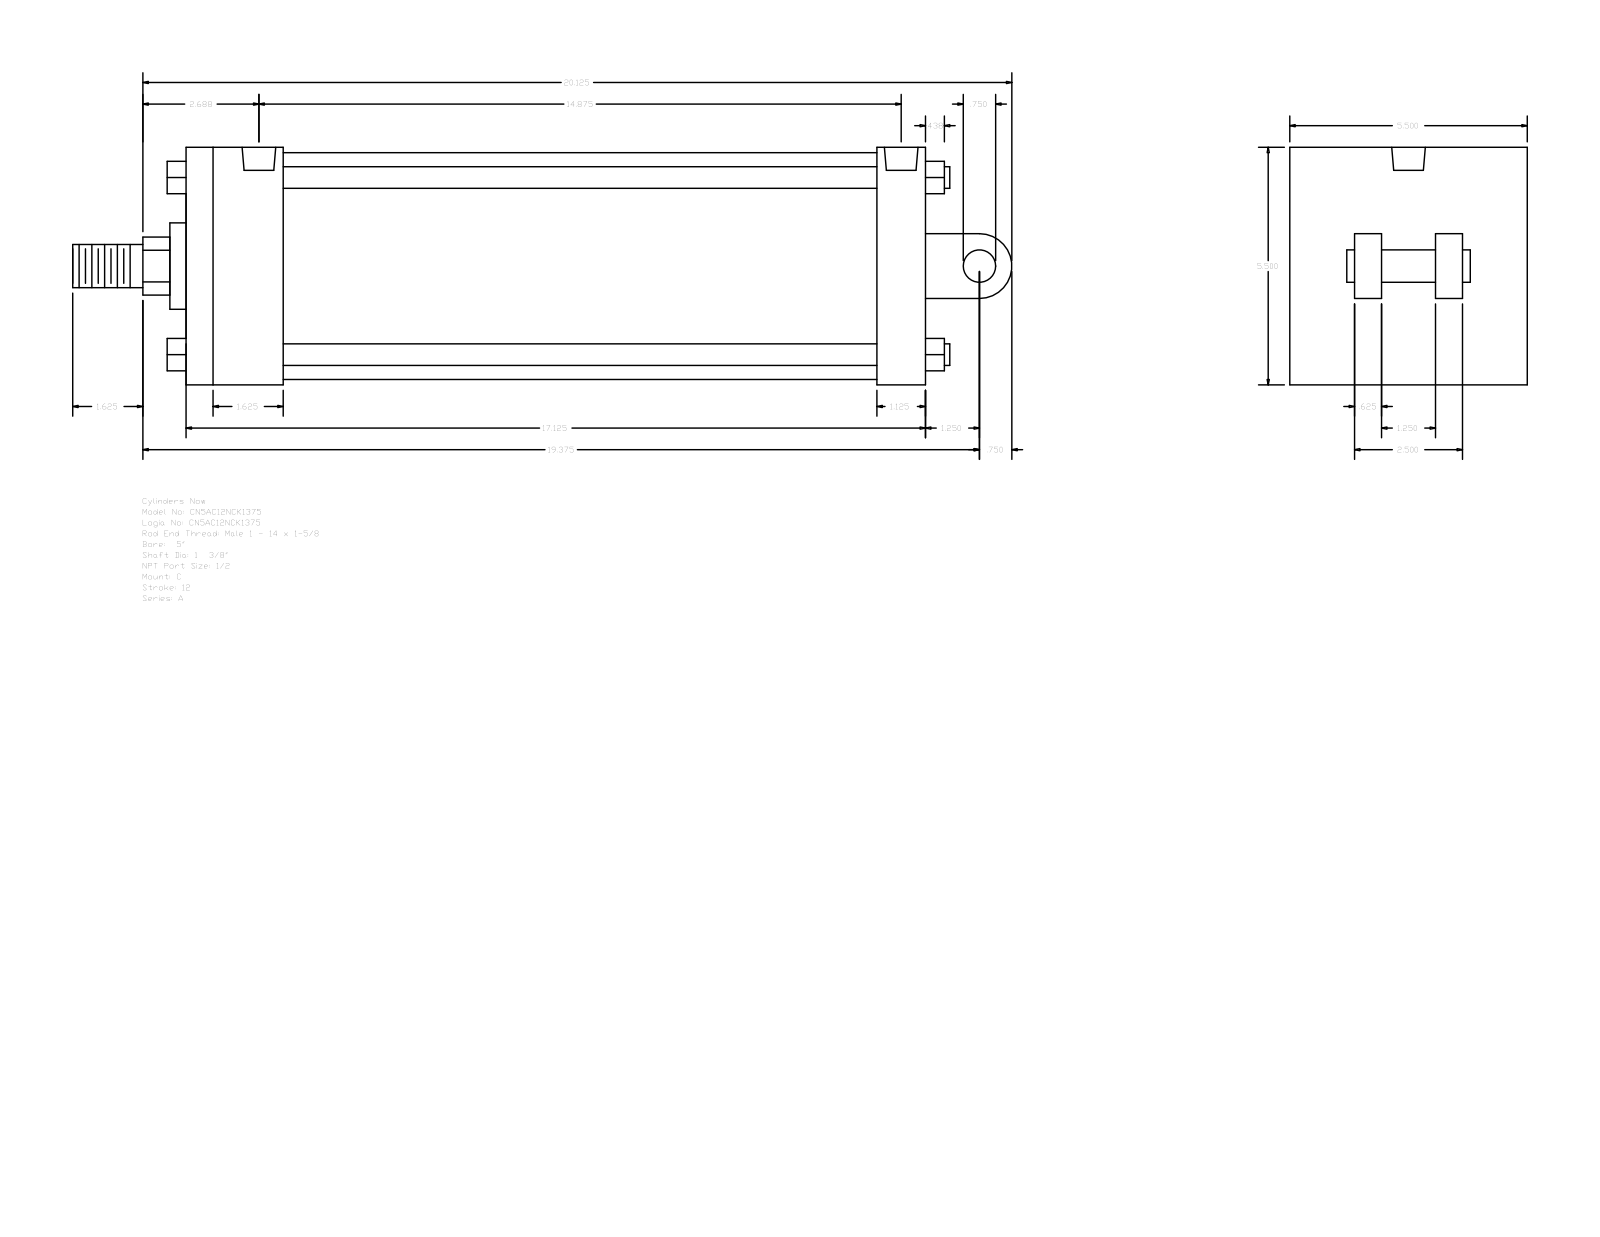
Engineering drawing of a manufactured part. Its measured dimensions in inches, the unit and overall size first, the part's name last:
Units: inches
Overall size (bounding box): 21.75 × 5.5 × 5.5
Round holes (diameter × count): ⌀0.344 ×4, ⌀0.778 ×2
Round bosses / shafts (diameter × count): ⌀0.5 ×4, ⌀5.25 ×1, ⌀2 ×1, ⌀1.375 ×1, ⌀1 ×1, ⌀0.75 ×1
Partial cylindrical surfaces — rounded edges, fillets, slot ends (radius × count): R0.672 ×1, R0.75 ×1
Main face-to-face distances: 5.5, 17.125, 2.25, 1.125, 16, 13.75, 14.875, 1.5, 2.125, 4
Hole centre spacings: 0.094, 14.687, 14.781, 14.875
Bodies: 0 solids, 135 faces (102 planar, 33 cylindrical, 0 other)
Part name (STEP PRODUCT): A_C__0500_1.375
STEP written by: GSSL Pune (CONFIG_CONTROL_DESIGN)
